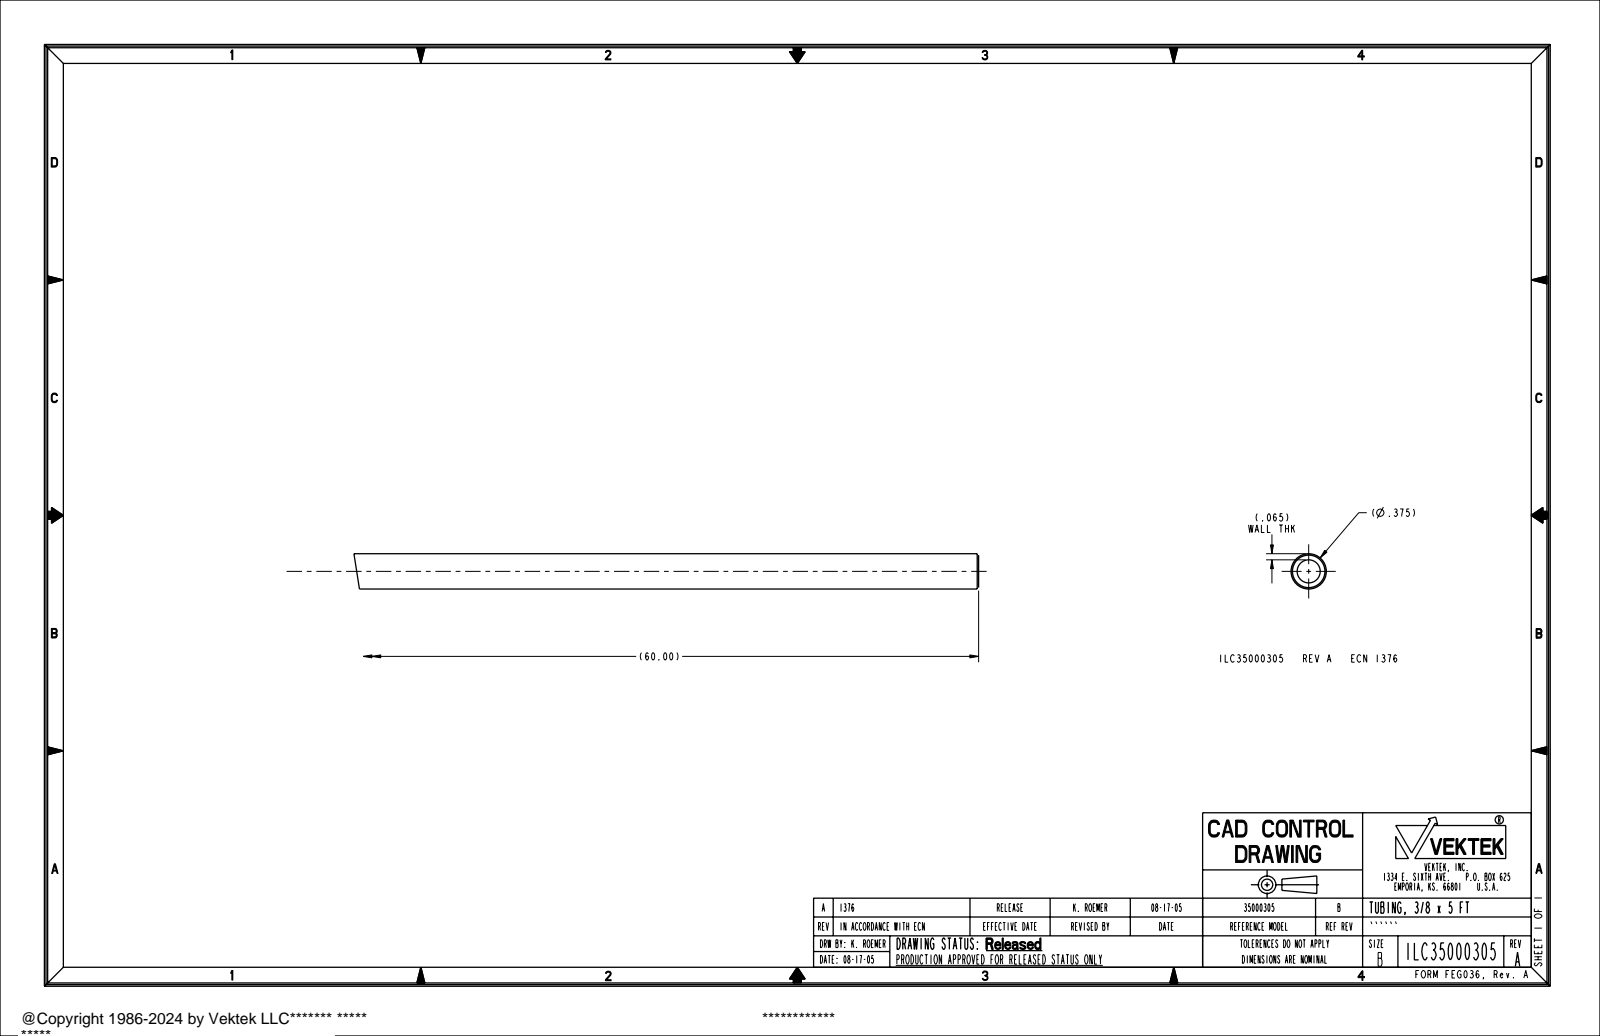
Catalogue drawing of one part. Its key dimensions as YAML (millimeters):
part_name: "ILC35000305"
step_written_by: "PRO/ENGINEER BY PARAMETRIC TECHNOLOGY CORPORATION, 2004290 (AUTOMOTIVE_DESIGN_CC2)"
units: millimeters
bodies: {solids: 1, faces: 10, planar: 2, cylindrical: 4, other: 4}
overall_size: [1524, 9.5, 9.5]
volume: 62240
surface_area: 75480
round_holes:
  - {diameter: 6.2, count: 1}
round_bosses_or_shafts:
  - {diameter: 9.5, count: 1}
face_to_face_distances: [1524]
